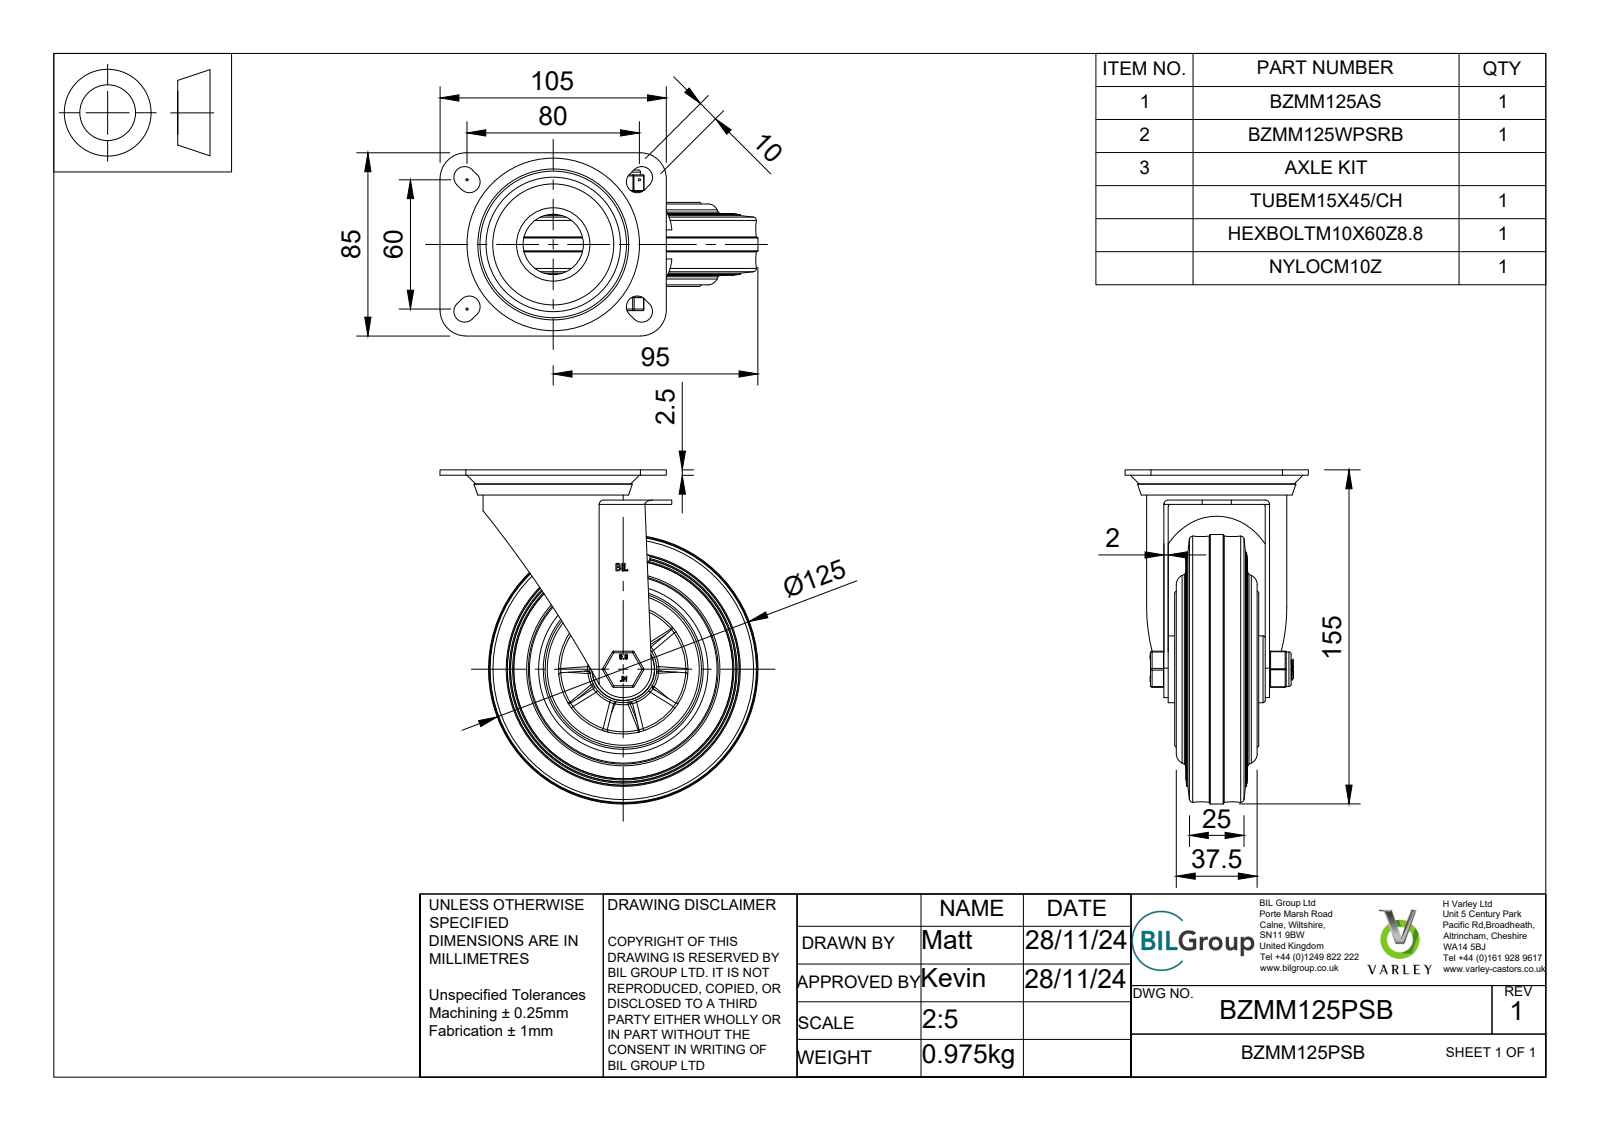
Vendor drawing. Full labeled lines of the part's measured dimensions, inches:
Part name (STEP PRODUCT): BZMM125PSB v3; BZMM125AS - 2 v2; ZINC PLATED, PRESSED STEEL TOP PLATE; ZINC PLATED, PRESSED STEEL FORKS (+8 more)
STEP written by: Autodesk Translation Framework v13.20.0.188 (AP242_MANAGED_MODEL_BASED_3D_ENGINEERING_MIM_LF)
Units: inches
Bodies: 19 solids, 766 faces (221 planar, 156 cylindrical, 389 other)
Overall size (bounding box): 6.102 × 5.807 × 3.346
Volume: 24.09 in³ · Surface area: 225.2 in²
Round holes (diameter × count): ⌀0.394 ×1, ⌀0.402 ×1, ⌀0.406 ×1, ⌀0.472 ×1, ⌀0.591 ×1, ⌀0.598 ×1, ⌀0.896 ×1, ⌀1.102 ×1, ⌀1.142 ×1, ⌀2.362 ×1, ⌀2.402 ×1, ⌀2.657 ×1
Round bosses / shafts (diameter × count): ⌀0.157 ×8, ⌀4.921 ×1, ⌀2.559 ×1, ⌀1.929 ×1, ⌀1.339 ×1, ⌀1.22 ×1, ⌀1.138 ×1, ⌀0.63 ×1
Partial cylindrical surfaces — rounded edges, fillets, slot ends (radius × count): R0.02 ×18, R0.03 ×12, R0.197 ×8, R0.039 ×4, R0.472 ×4, R0.079 ×2, R0.815 ×2, R0.369 ×1
Main face-to-face distances: 0.079, 0.197, 0.098, 0.374, 0.177, 0.453, 0.295, 1.85, 0.276, 0.256
